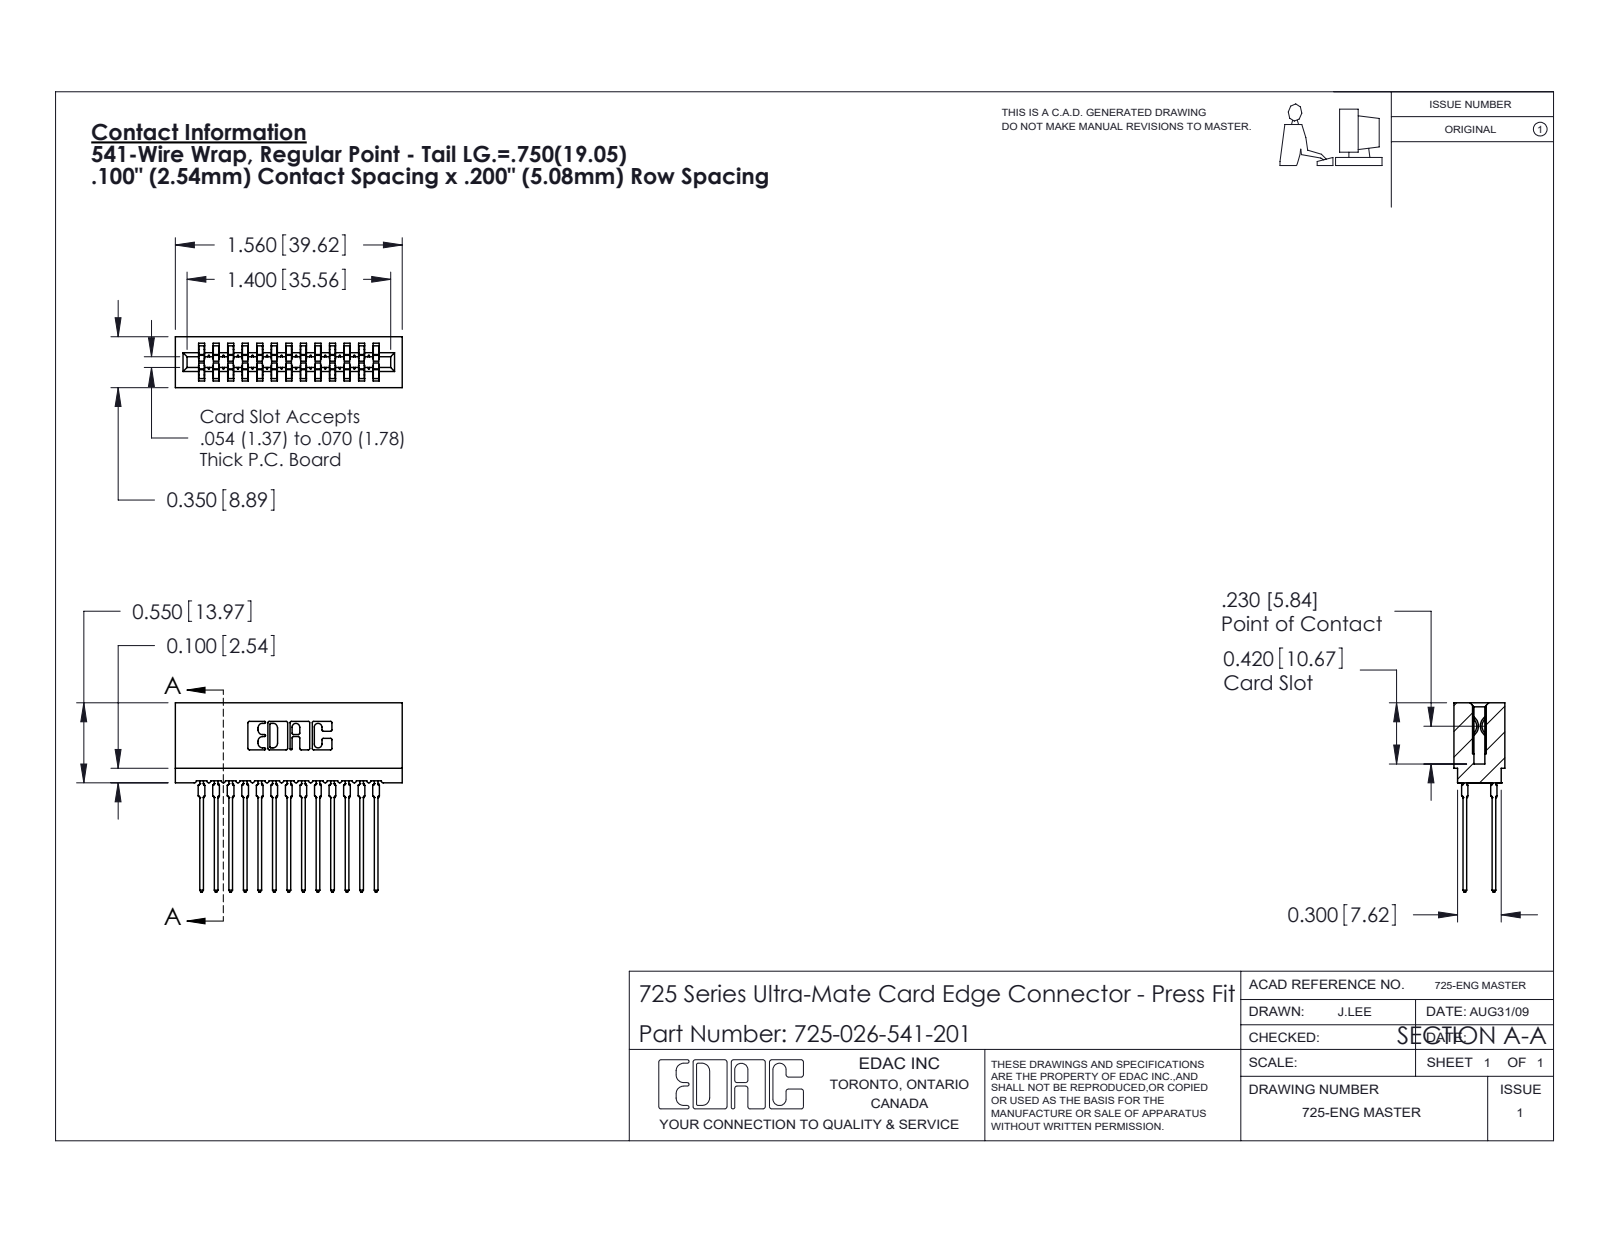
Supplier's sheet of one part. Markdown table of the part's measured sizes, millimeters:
| quantity | value |
| --- | --- |
| part name | 725-026-541-201; 745-292-001_541; 725 Part_Insulator Option - 01 |
| STEP written by | SolidWorks 2020 (CONFIG_CONTROL_DESIGN) |
| units | millimeters |
| bodies | 27 solids, 2422 faces (1251 planar, 495 cylindrical, 676 other) |
| overall size | 39.6 × 33 × 8.9 |
| volume | 3 410 mm³ |
| surface area | 7 110 mm² |
| partial cylindrical surfaces (radius × count) | 0.5 × 52, 0.4 × 26, 0.3 × 22, 0.1 × 8, 0.3 × 8, 0.2 × 6, 0.8 × 6, 0.7 × 3 |
| main face-to-face distances | 5.1, 2.5, 7.6, 10.2, 1.6, 7.3, 12.7, 15.2, 8.9, 2.2 |
